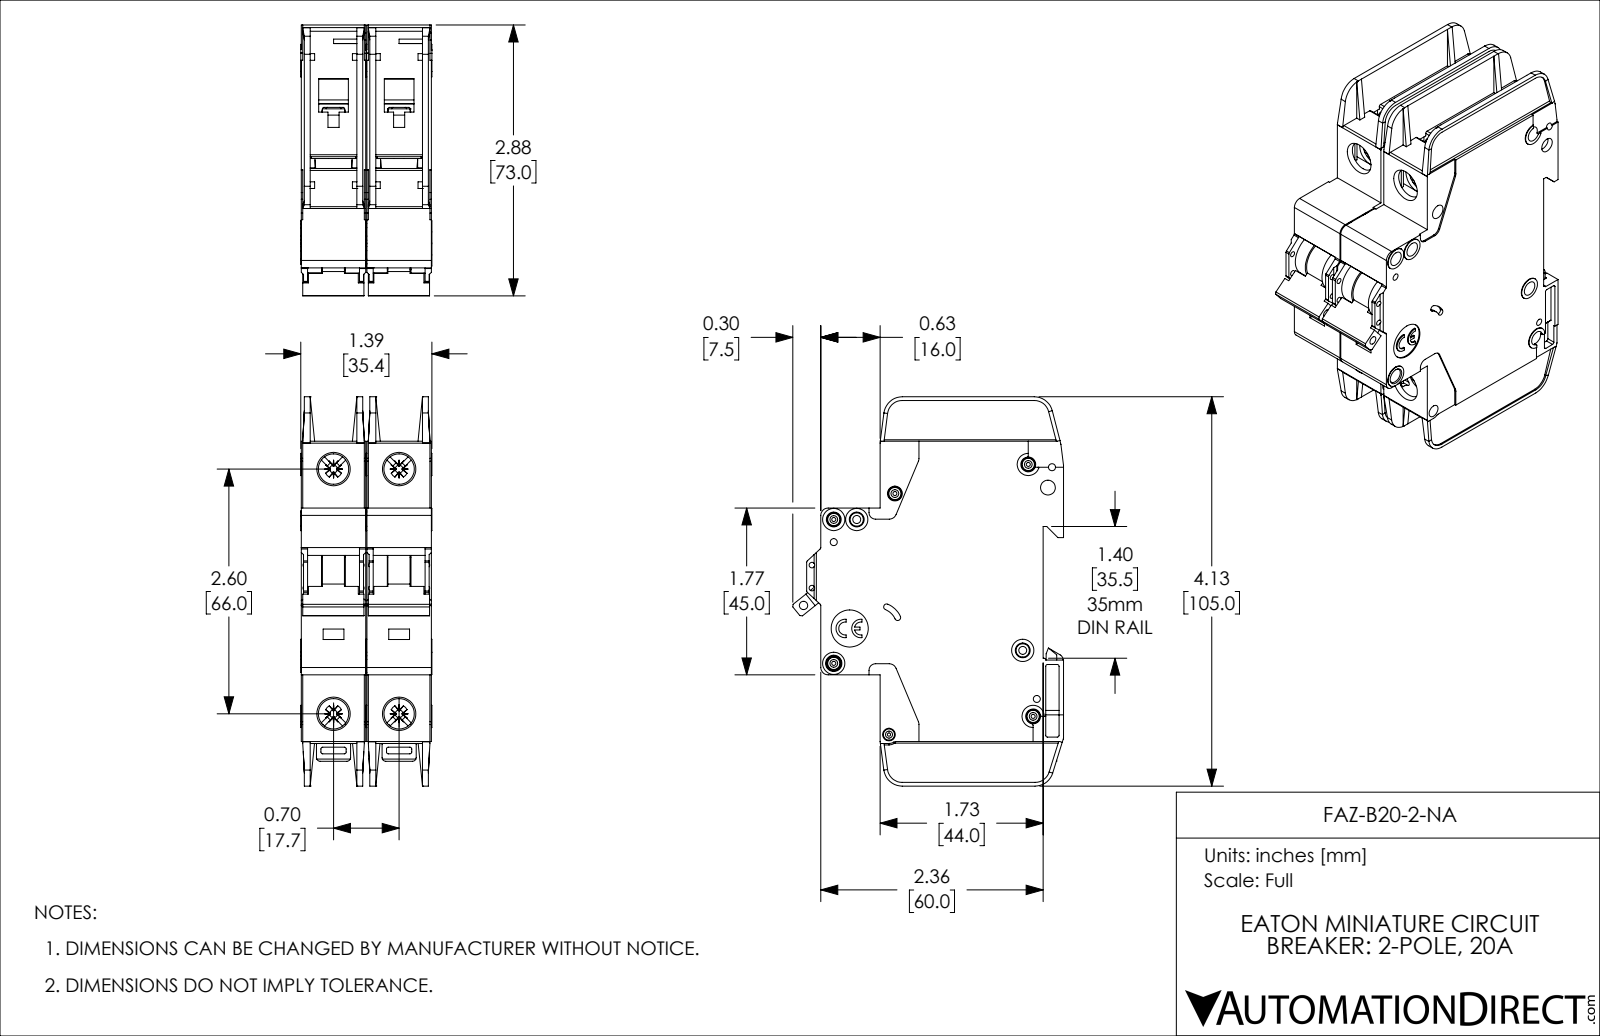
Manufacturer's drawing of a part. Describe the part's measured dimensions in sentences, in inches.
The part is named "FAZ-B20-2-NA". Its 3-D file was written by "SolidWorks 2019 (AUTOMOTIVE_DESIGN)". It is 2 solids with 2254 faces: 1342 planar, 714 cylindrical and 198 other. Overall it measures 4.134 by 2.876 by 1.394 inches. Its volume is 9.365 cubic inches and its surface area 82.01 square inches. Round holes: 8 of diameter 0.157, 5 of diameter 0.043, 4 of diameter 0.075, 4 of diameter 0.323, 2 of diameter 0.059, 2 of diameter 0.085, 1 of diameter 0.035, 1 of diameter 0.089, 1 of diameter 0.098, 1 of diameter 0.134, 1 of diameter 0.394. Round bosses or shafts: 5 of diameter 0.13, 4 of diameter 0.236, 3 of diameter 0.118, 2 of diameter 0.098. Partial cylindrical surfaces (rounded edges, fillets, slot ends): 57 of radius 0.02, 20 of radius 0.016, 14 of radius 0.039, 10 of radius 0.079, 8 of radius 0.043, 5 of radius 0.008, 5 of radius 0.197, 4 of radius 0.01. The main face-to-face distances are 0.697, 0.047, 0.685, 0.591, 0.094, 0.638, 0.543, 1.382, 0.744, 0.65. The hole center spacings are 0.244, 0.537, 0.697, 0.87, 2.598, 2.69, 0.189, 0.199.
